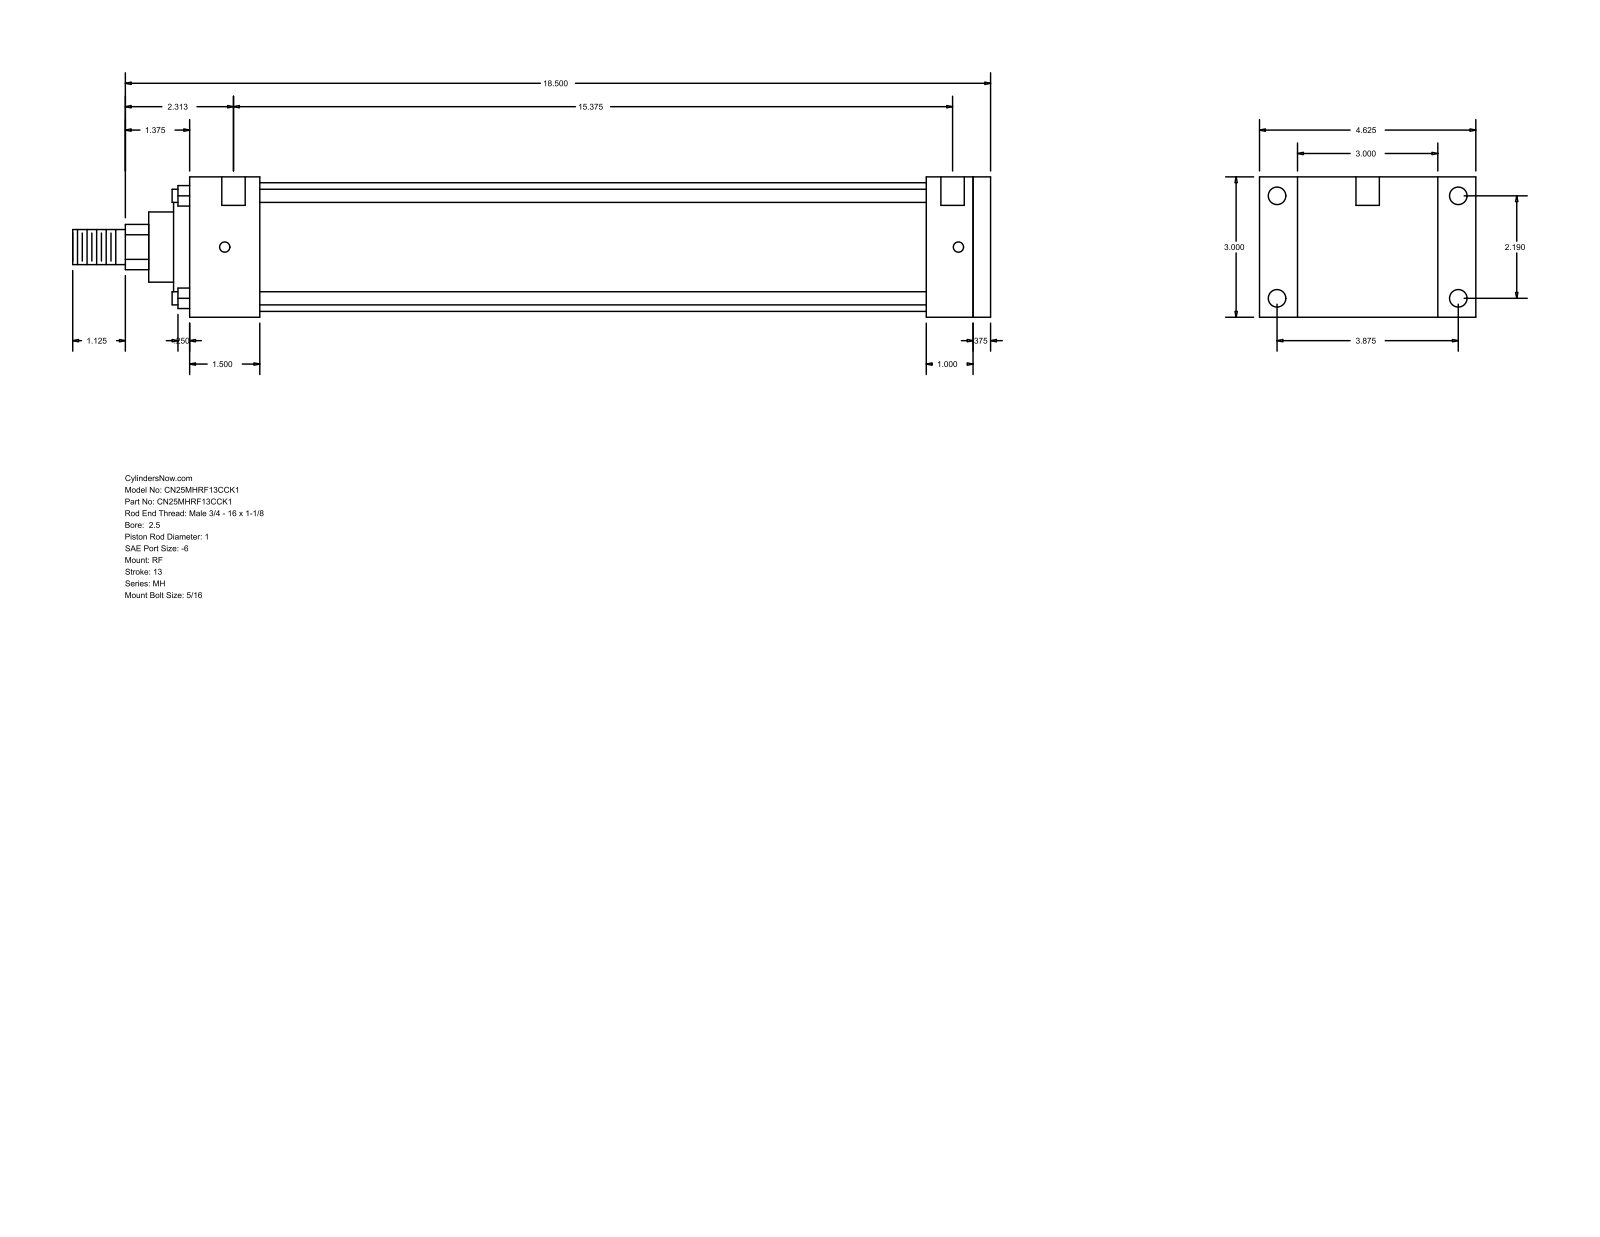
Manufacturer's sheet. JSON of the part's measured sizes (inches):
{"part_name": "MH_RF__0250_1", "step_written_by": "GSSL Pune (CONFIG_CONTROL_DESIGN)", "units": "inches", "bodies": {"solids": 0, "faces": 94, "planar": 65, "cylindrical": 29, "other": 0}, "overall_size": [19.625, 4.625, 3], "round_holes": [[0.219, 4], [0.375, 4], [0.5, 2]], "round_bosses_or_shafts": [[0.281, 4], [2.75, 1], [2.375, 1], [1.5, 1], [1, 1], [0.75, 1]], "partial_cylinders_radius": [[0.484, 1]], "face_to_face_distances": [3, 0.375, 17.125, 16.75, 1, 1.375, 15.75, 1.5, 14.25, 15.25], "hole_center_spacings": [2.19, 3.875, 4.451, 15.687, 0.125, 0.187, 15.375, 15.5]}
